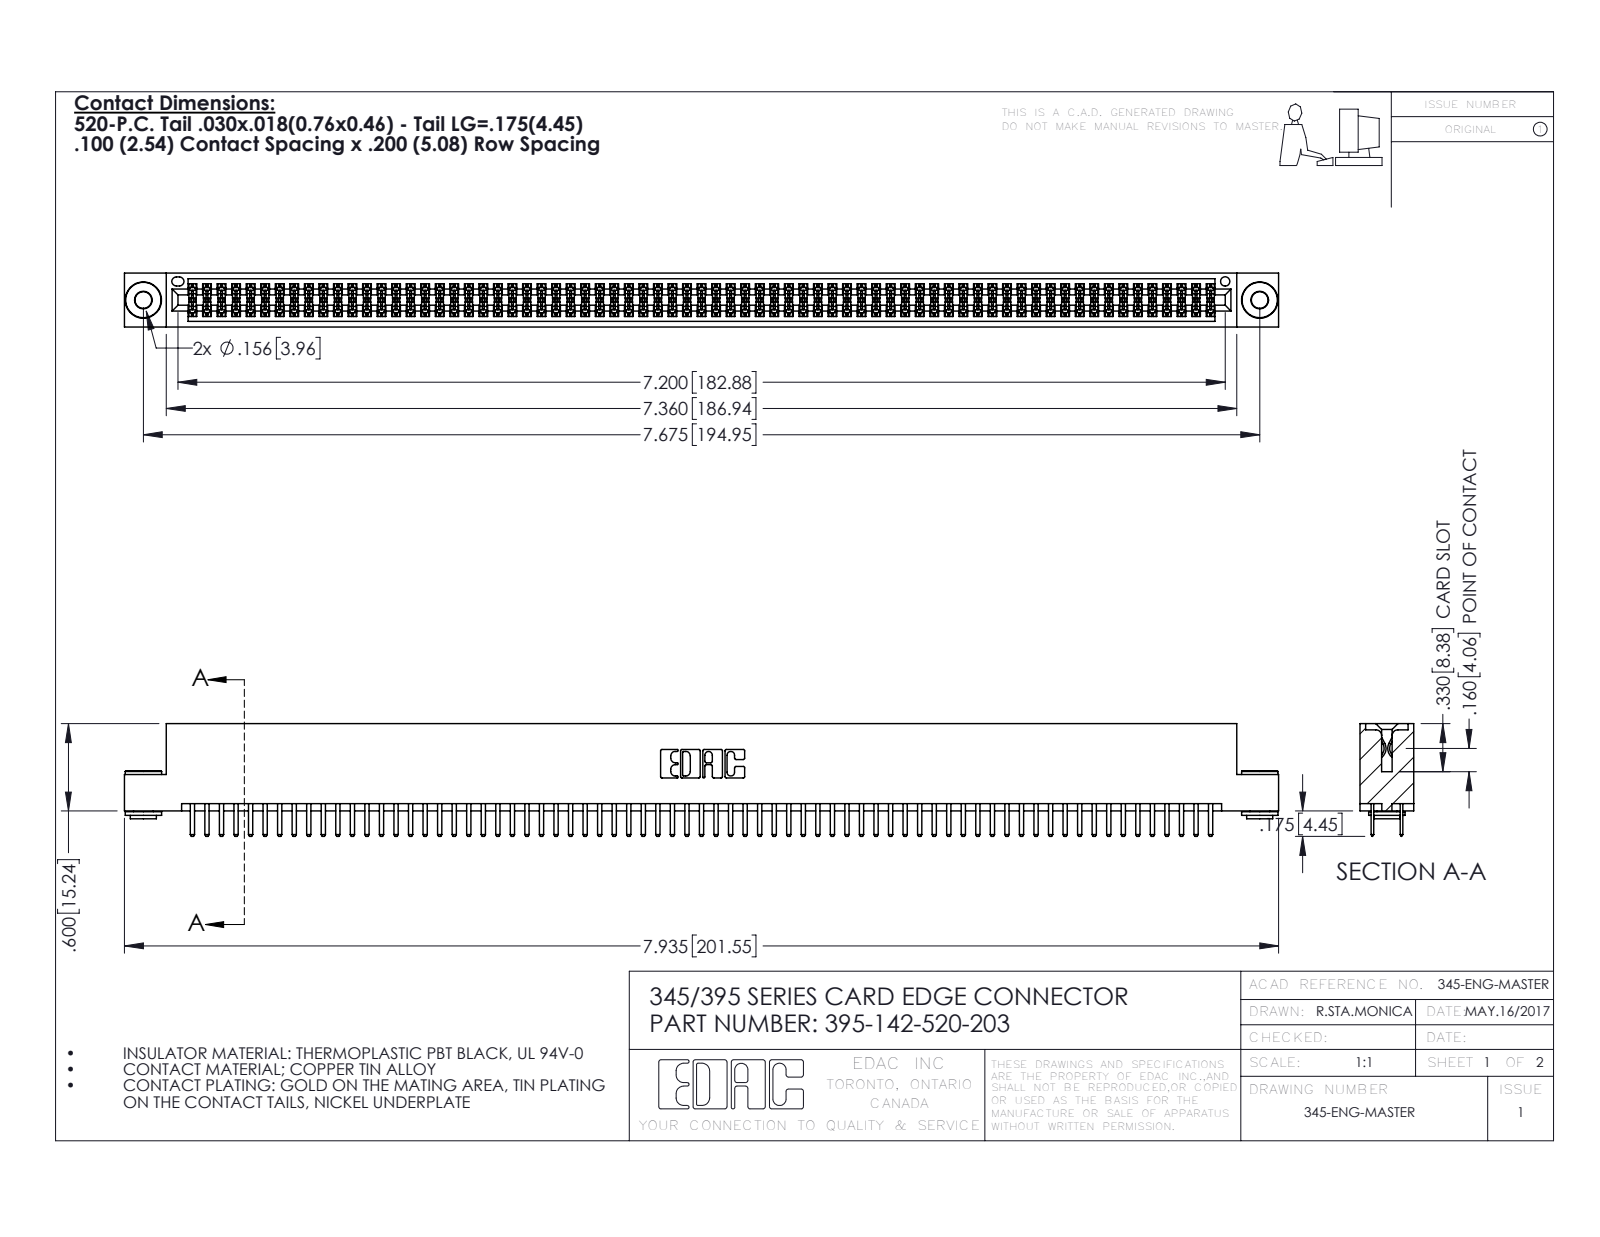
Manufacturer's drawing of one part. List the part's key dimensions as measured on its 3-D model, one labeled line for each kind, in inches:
Part name (STEP PRODUCT): 395-142-520-203; 345 Part_Flush Mounting Lugs - 0.156 Dia-TH; 345-250-002_345-250-002-102; 345-292-001_345-293-120
STEP written by: SolidWorks 2016 (CONFIG_CONTROL_DESIGN)
Units: inches
Bodies: 145 solids, 7832 faces (5060 planar, 2764 cylindrical, 8 other)
Overall size (bounding box): 7.935 × 0.775 × 0.37
Volume: 1.209 in³ · Surface area: 46.36 in²
Round holes (diameter × count): ⌀0.116 ×2, ⌀0.156 ×2, ⌀0.064 ×1
Round bosses / shafts (diameter × count): ⌀0.25 ×2, ⌀0.18 ×2, ⌀0.136 ×2
Partial cylindrical surfaces — rounded edges, fillets, slot ends (radius × count): R0.006 ×213, R0.01 ×146, R0.01 ×22, R0.007 ×6, R0.031 ×6, R0.026 ×3, R0.014 ×2, R0.019 ×2
Main face-to-face distances: 0.072, 0.298, 0.2, 0.37, 0.025, 0.098, 0.272, 0.225, 0.022, 0.072
Hole centre spacings: 0.27, 7.439, 7.675
